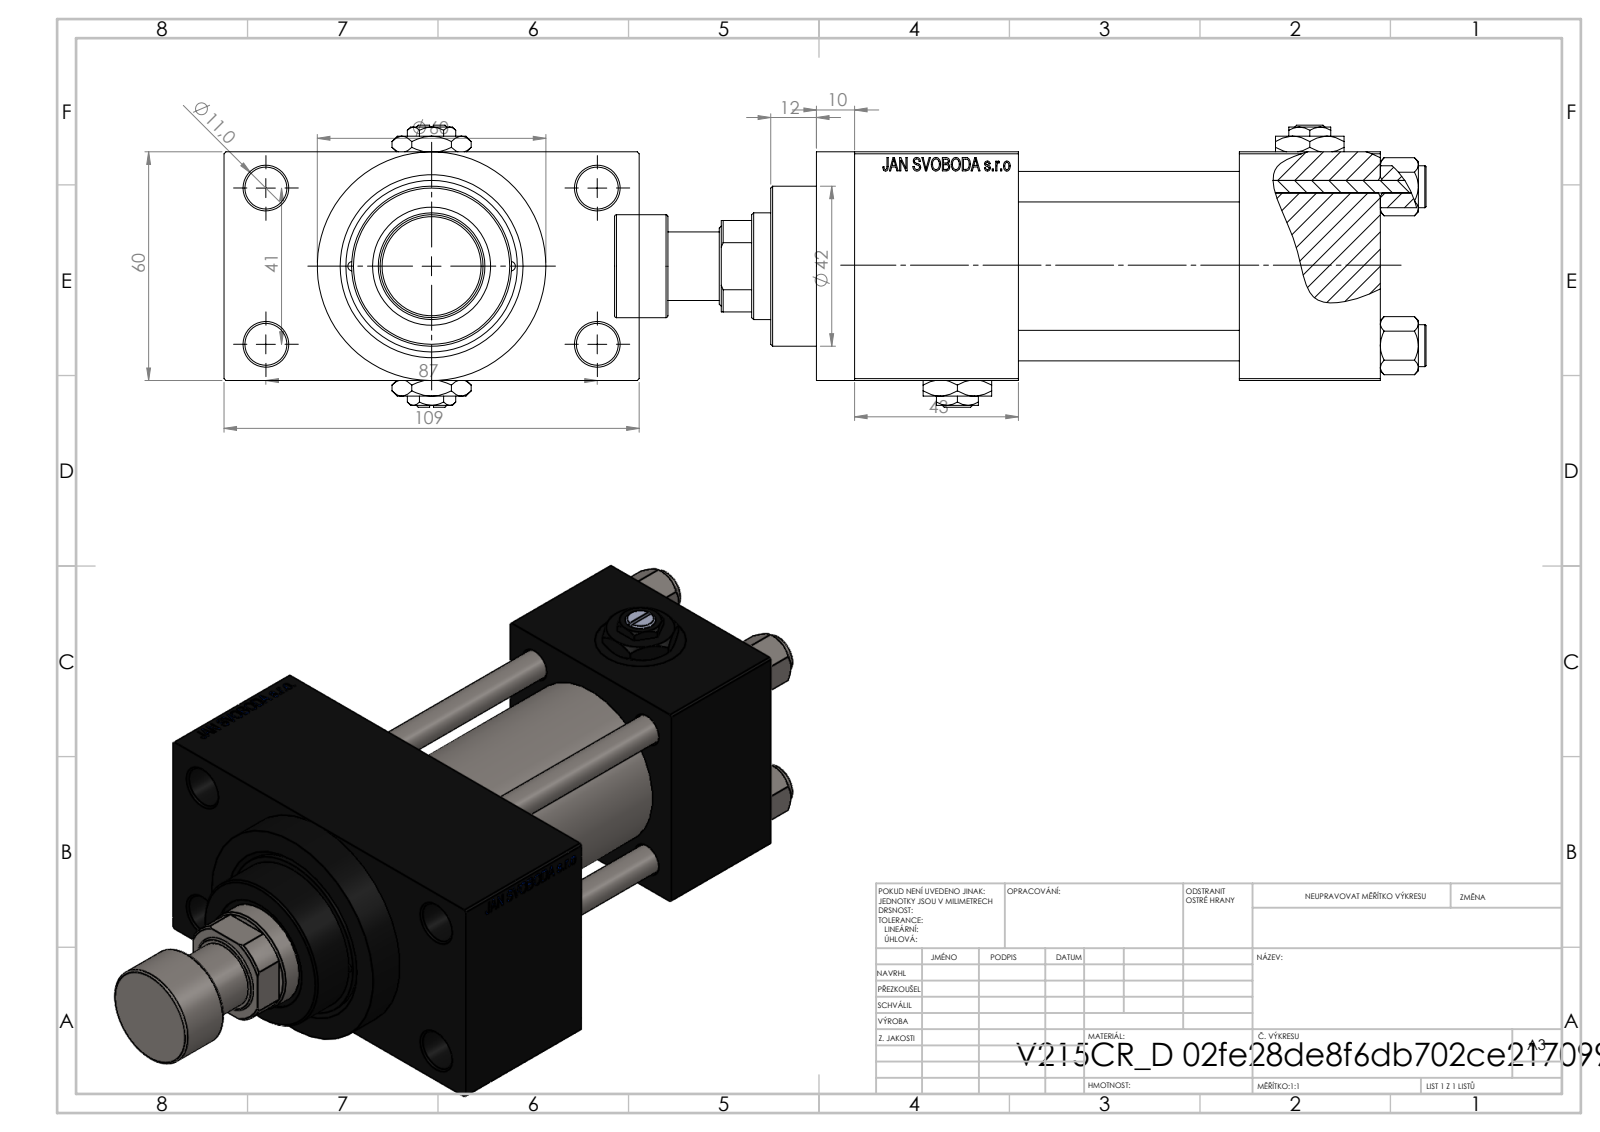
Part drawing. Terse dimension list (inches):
name: V215CR_VCP_D; V215CR_ROD_END_F; V215CR_D_TYCINKA; NUT_M5_D (+3 more)
written by: SolidWorks 2019 (CONFIG_CONTROL_DESIGN)
unit: in
bodies: 14 solids, 1213 faces (550 planar, 97 cylindrical, 566 other)
size: 8.386 × 4.291 × 2.913
volume: 33.47 in³; area: 205.9 in²
holes: 4× ⌀0.315, 4× ⌀0.433, 2× ⌀0.098, 2× ⌀0.276, 2× ⌀0.656, 2× ⌀0.945, 1× ⌀0.728, 1× ⌀1.102, 1× ⌀1.22, 1× ⌀1.575, 1× ⌀1.772
bosses: 4× ⌀0.433, 1× ⌀2.362, 1× ⌀1.811, 1× ⌀1.654, 1× ⌀1.063, 1× ⌀0.709
face distances: 2.362, 3.327, 0.965, 2.283, 1.457, 3.74, 5.433, 3.976, 1.693, 4.291
hole spacings: 0.821, 0.892, 1.161, 1.206, 1.642, 1.832, 1.856, 1.893
